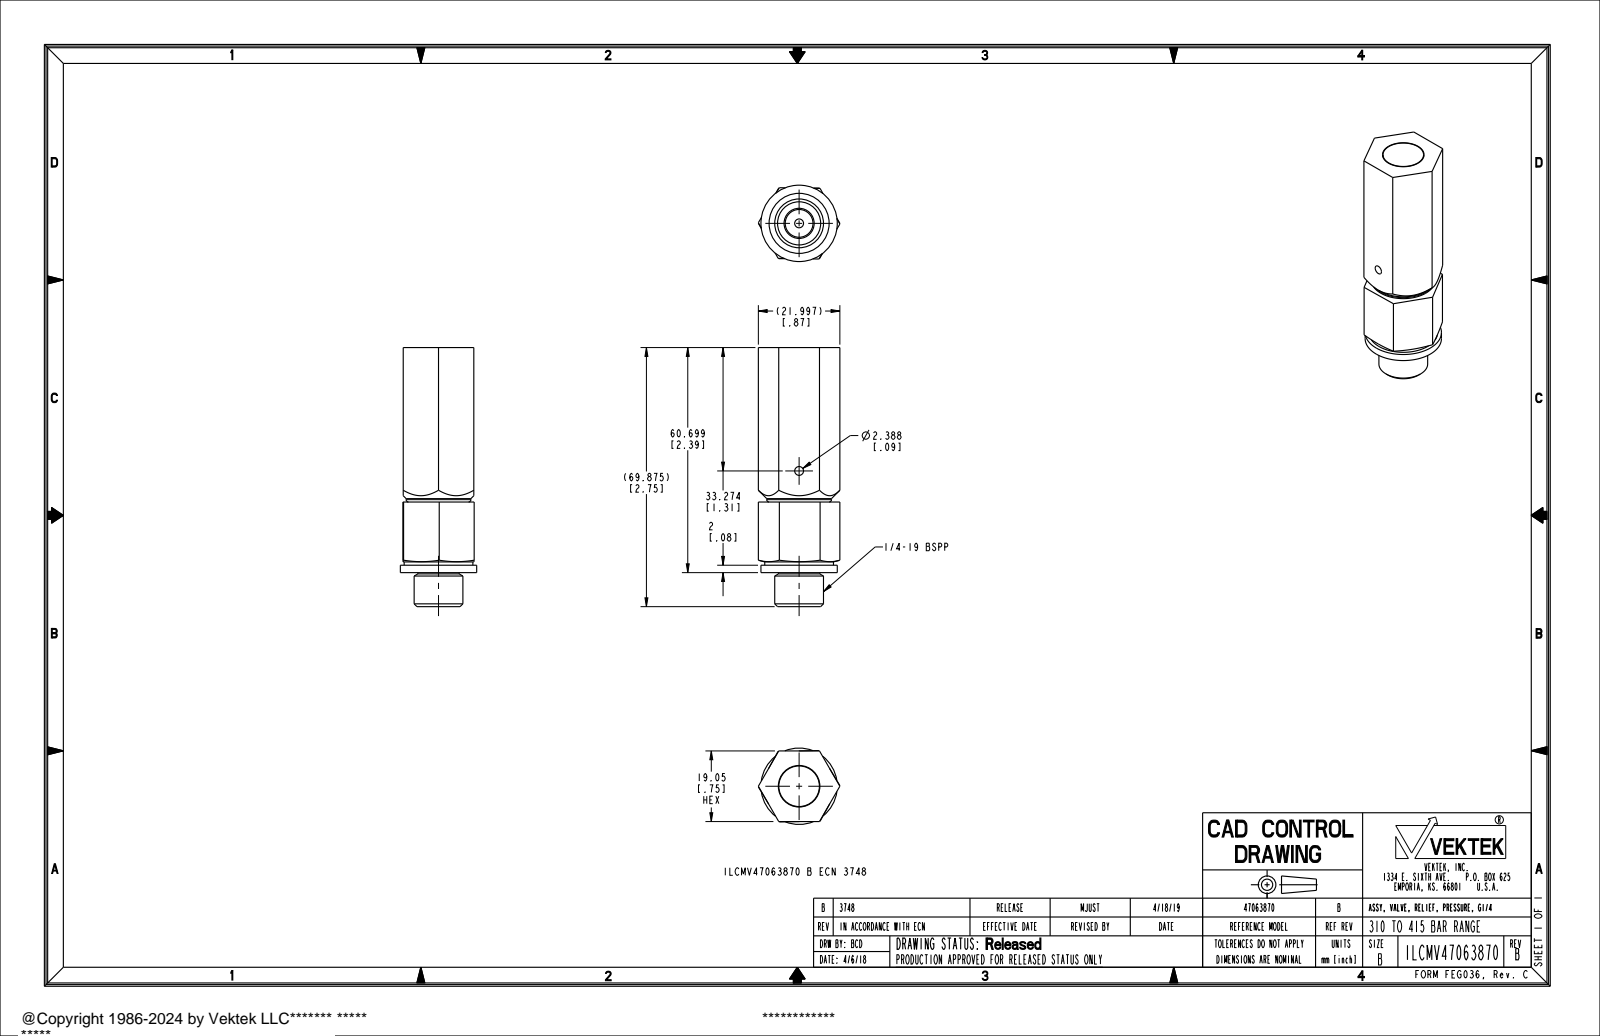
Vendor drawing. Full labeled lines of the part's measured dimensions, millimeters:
Part name (STEP PRODUCT): ILCMV47063870
STEP written by: PRO/ENGINEER BY PARAMETRIC TECHNOLOGY CORPORATION, 2013320 (AUTOMOTIVE_DESIGN)
Units: millimetres
Bodies: 1 solid, 61 faces (23 planar, 26 cylindrical, 12 other)
Overall size (bounding box): 69.88 × 22 × 20.6
Volume: 18 598 mm³ · Surface area: 6 384 mm²
Round holes (diameter × count): ⌀2.39 ×2, ⌀7.49 ×1, ⌀11.2 ×1, ⌀16.2 ×1
Round bosses / shafts (diameter × count): ⌀20.6 ×1, ⌀18.54 ×1, ⌀17.48 ×1, ⌀13.16 ×1, ⌀11.15 ×1, ⌀10.95 ×1
Main face-to-face distances: 19.04, 19.06, 58.7, 17.04, 41.66, 2, 60.7, 11.18, 9.18, 28.22
